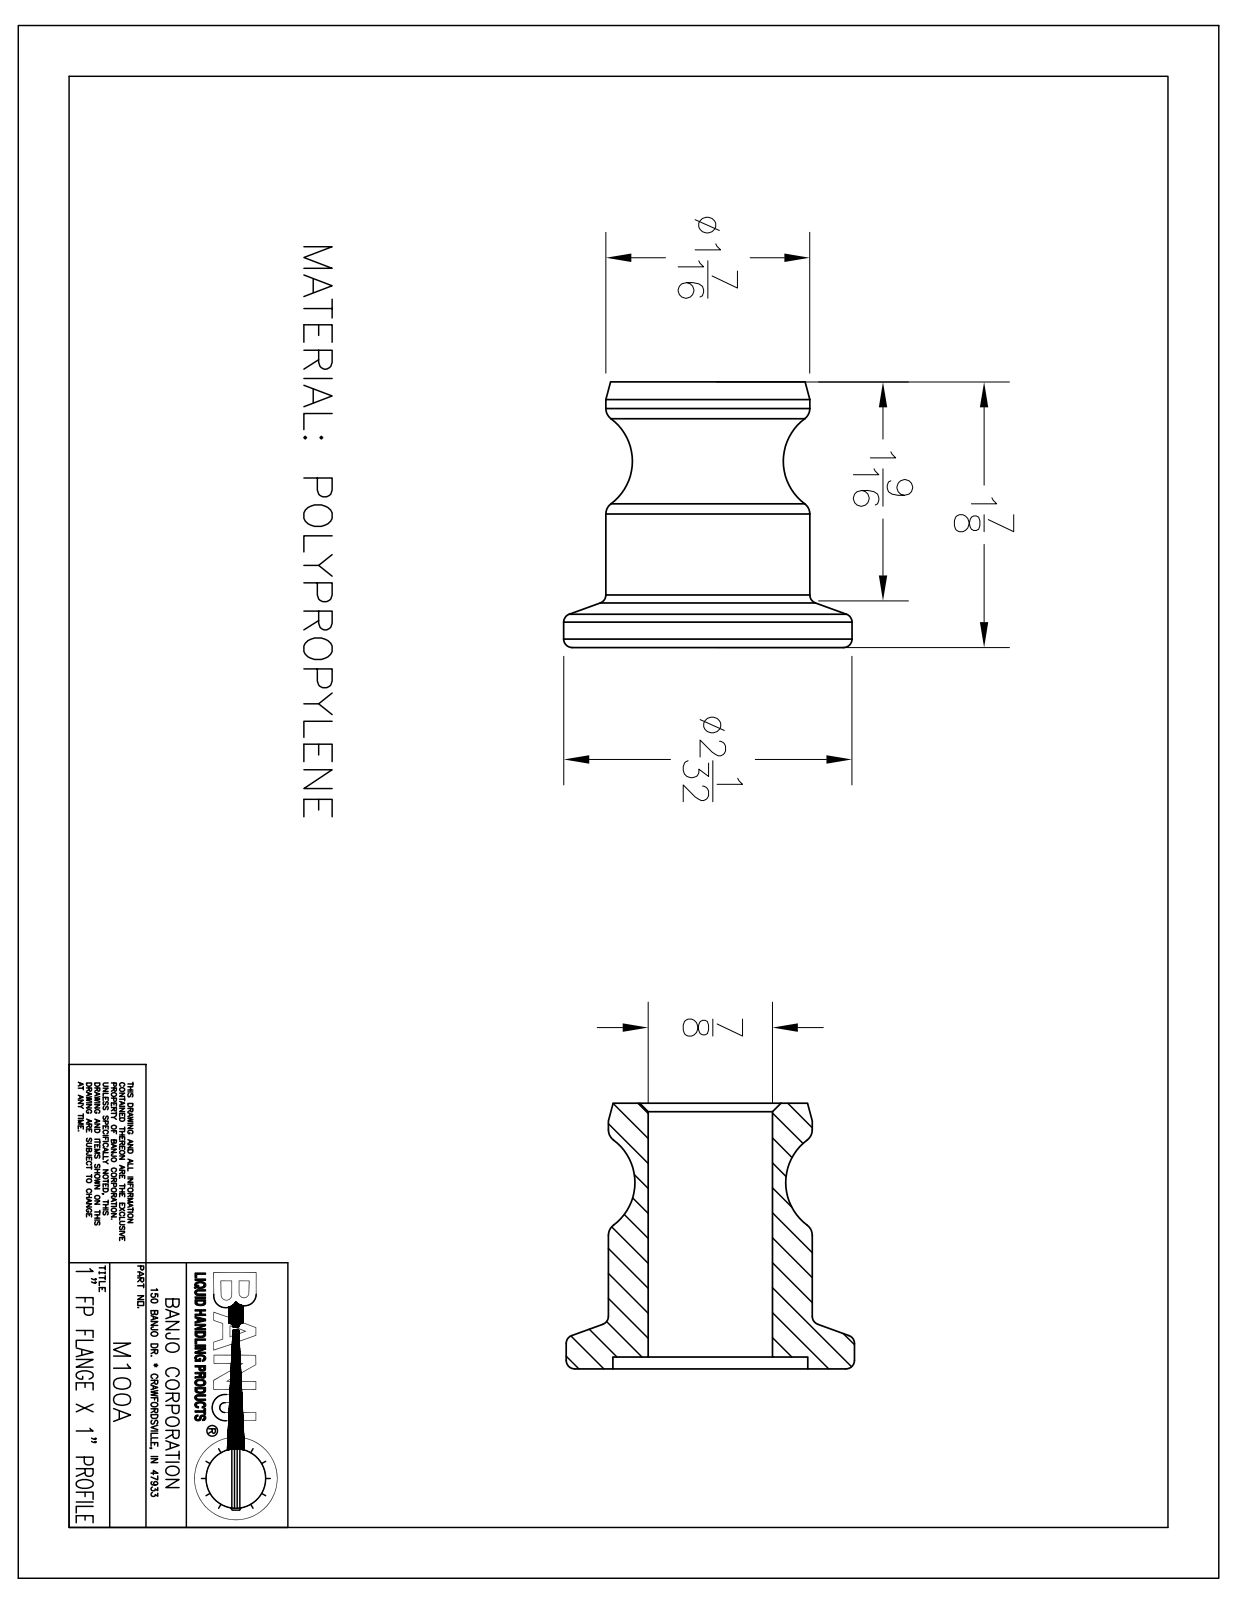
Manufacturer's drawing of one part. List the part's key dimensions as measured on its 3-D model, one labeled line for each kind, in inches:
Part name (STEP PRODUCT): M100A
STEP written by: Autodesk Inventor 2012 (AUTOMOTIVE_DESIGN)
Units: inches
Bodies: 1 solid, 295 faces (160 planar, 34 cylindrical, 101 other)
Overall size (bounding box): 2.04 × 2.04 × 1.88
Volume: 1.944 in³ · Surface area: 19.11 in²
Round holes (diameter × count): ⌀0.88 ×1, ⌀1.38 ×1
Round bosses / shafts (diameter × count): ⌀2.04 ×1, ⌀1.451 ×1
Partial cylindrical surfaces — rounded edges, fillets, slot ends (radius × count): R0.696 ×1
Main face-to-face distances: 0.084, 1.796, 1.88, 0.132, 1.147, 0.649, 0.733, 0.054, 0.154, 0.051
